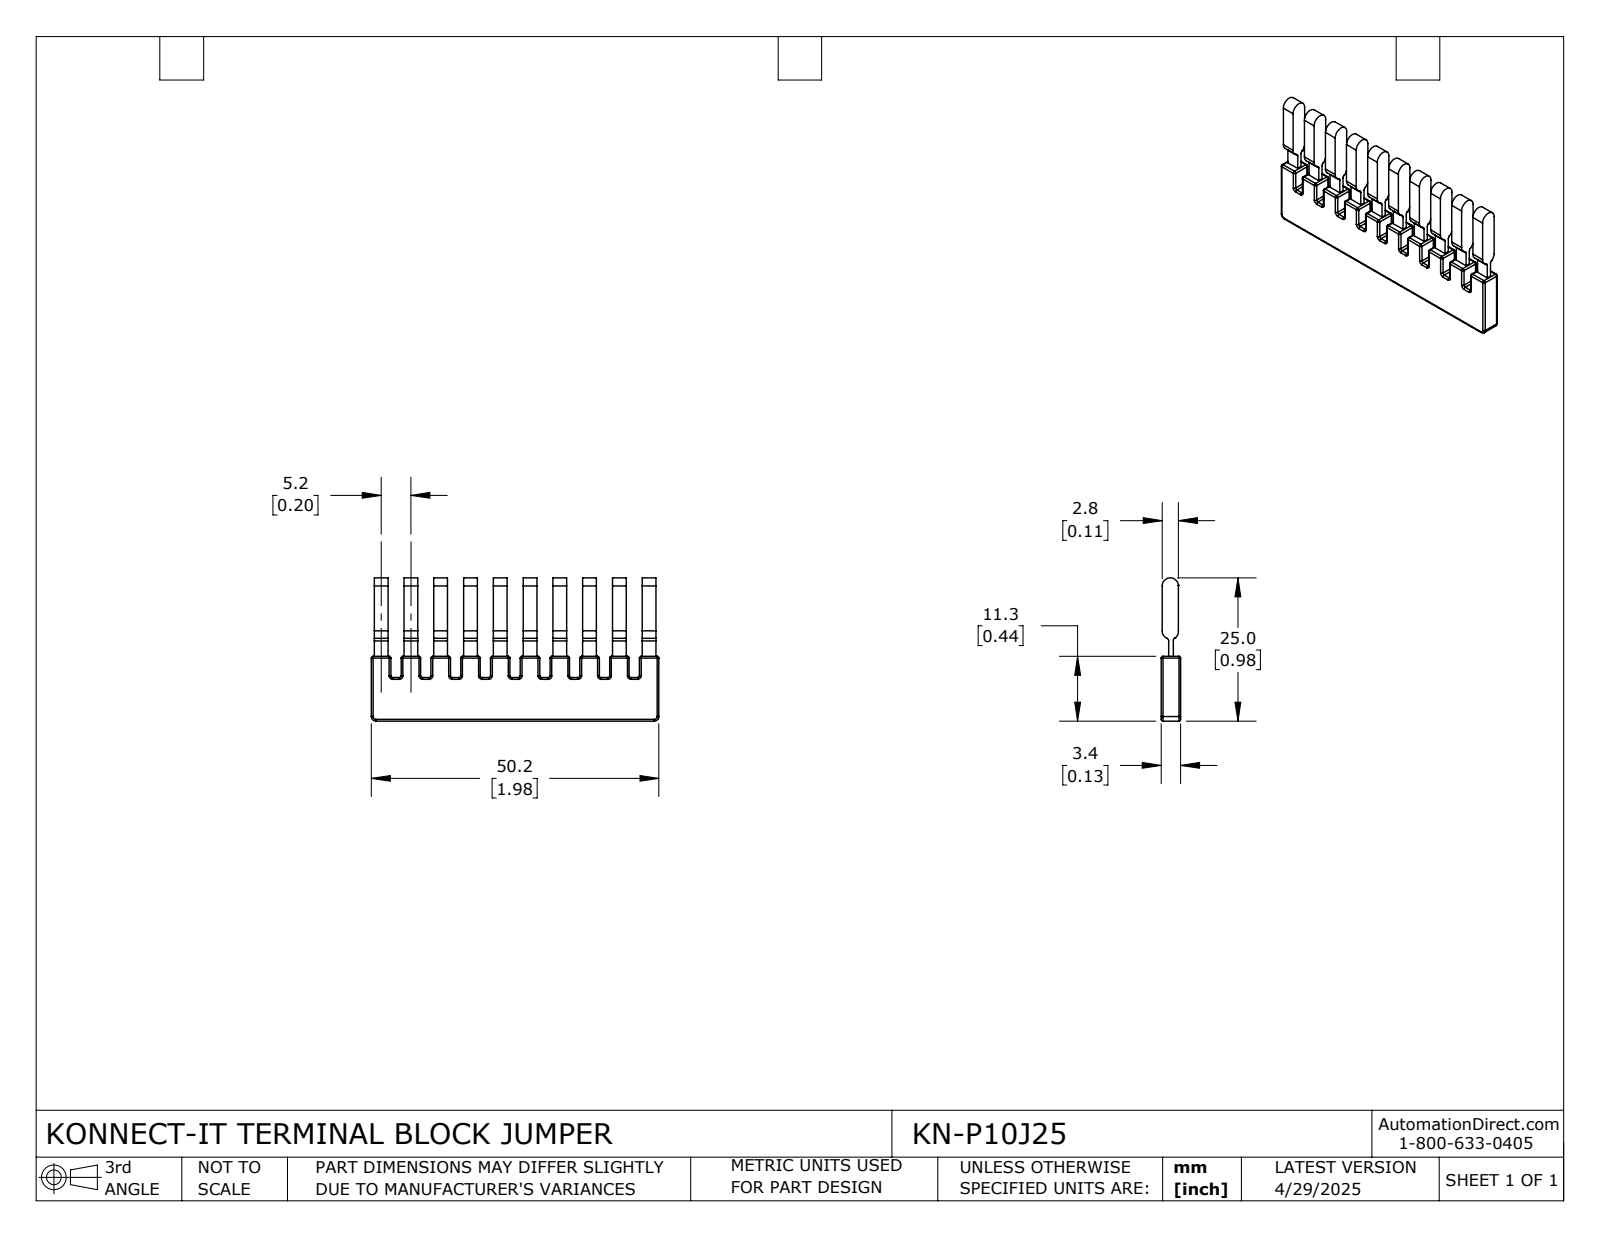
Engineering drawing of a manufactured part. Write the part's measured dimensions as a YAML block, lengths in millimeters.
part_name: "KN-P10J25"
step_written_by: "SolidWorks 2024 (CONFIG_CONTROL_DESIGN)"
units: millimeters
bodies: {solids: 1, faces: 377, planar: 118, cylindrical: 179, other: 80}
overall_size: [50.2, 25, 3.4]
volume: 2466
surface_area: 2912
partial_cylinders:
  - {radius: 0.3, count: 84}
  - {radius: 2, count: 5}
  - {radius: 0.5, count: 2}
  - {radius: 0.8, count: 2}
  - {radius: 1.43, count: 2}
  - {radius: 1.3, count: 1}
face_to_face_distances: [5.2, 10.4, 3.4, 15.6, 20.8, 2.4, 26, 7.6, 2.8, 31.2]
